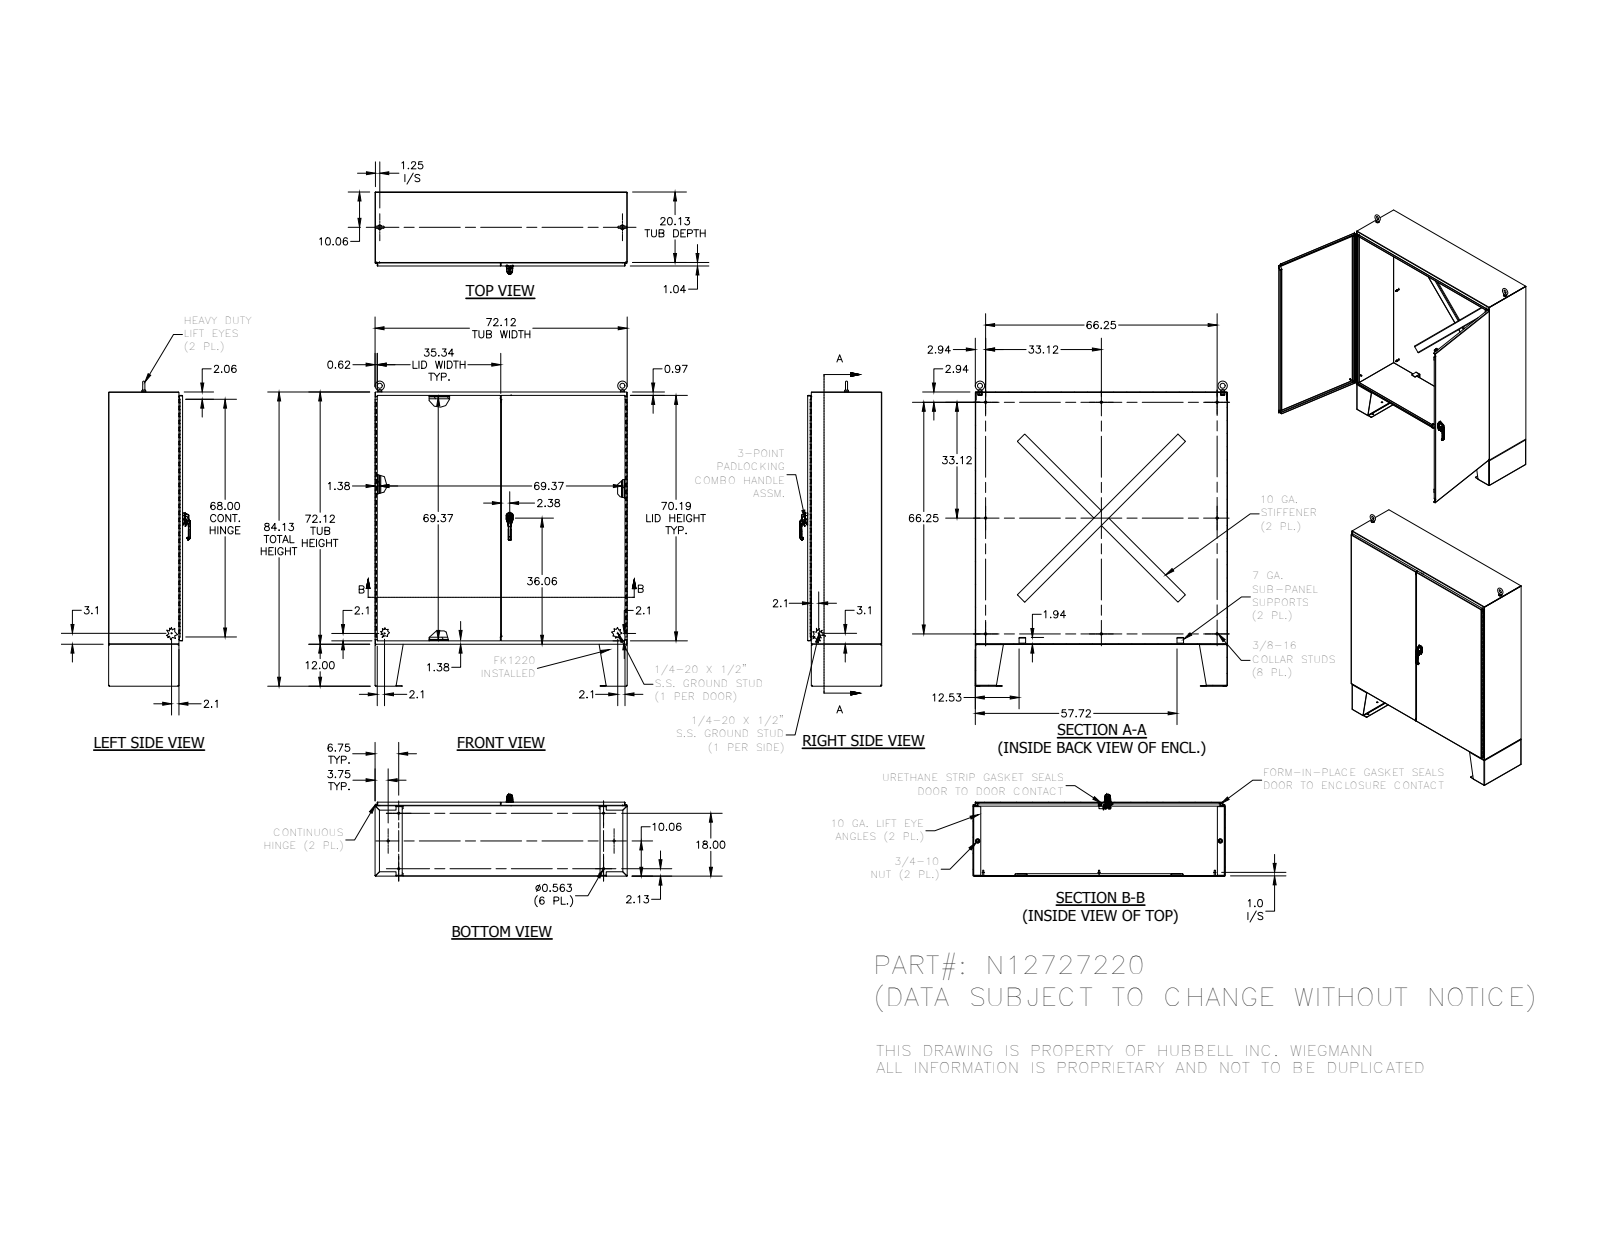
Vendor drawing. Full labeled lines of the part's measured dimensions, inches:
Part name (STEP PRODUCT): N12727220
STEP written by: SolidWorks 2018 (AUTOMOTIVE_DESIGN)
Units: inches
Bodies: 76 solids, 2596 faces (1528 planar, 768 cylindrical, 300 other)
Overall size (bounding box): 87.248 × 72.268 × 23.338
Volume: 1 955 in³ · Surface area: 39 686 in²
Round holes (diameter × count): ⌀0.563 ×18, ⌀0.277 ×8, ⌀0.2 ×4, ⌀0.125 ×3, ⌀0.28 ×3, ⌀0.241 ×2, ⌀0.25 ×2, ⌀0.252 ×2, ⌀0.4 ×2, ⌀0.45 ×2, ⌀0.642 ×2, ⌀0.813 ×2
Round bosses / shafts (diameter × count): ⌀0.33 ×8, ⌀0.625 ×5, ⌀0.25 ×5, ⌀0.625 ×3, ⌀0.337 ×3, ⌀1.25 ×2, ⌀1.12 ×2, ⌀1 ×2
Partial cylindrical surfaces — rounded edges, fillets, slot ends (radius × count): R0.031 ×24, R0.094 ×23, R0.219 ×22, R0.05 ×18, R0.025 ×16, R0.125 ×15, R0.03 ×13, R0.067 ×8
Main face-to-face distances: 0.094, 21.067, 72.031, 20.973, 21.16, 72.125, 71.938, 0.125, 0.125, 20.031
Hole centre spacings: 2.041, 5, 16.876, 18.75, 19.405, 58.393, 60.888, 62.087
